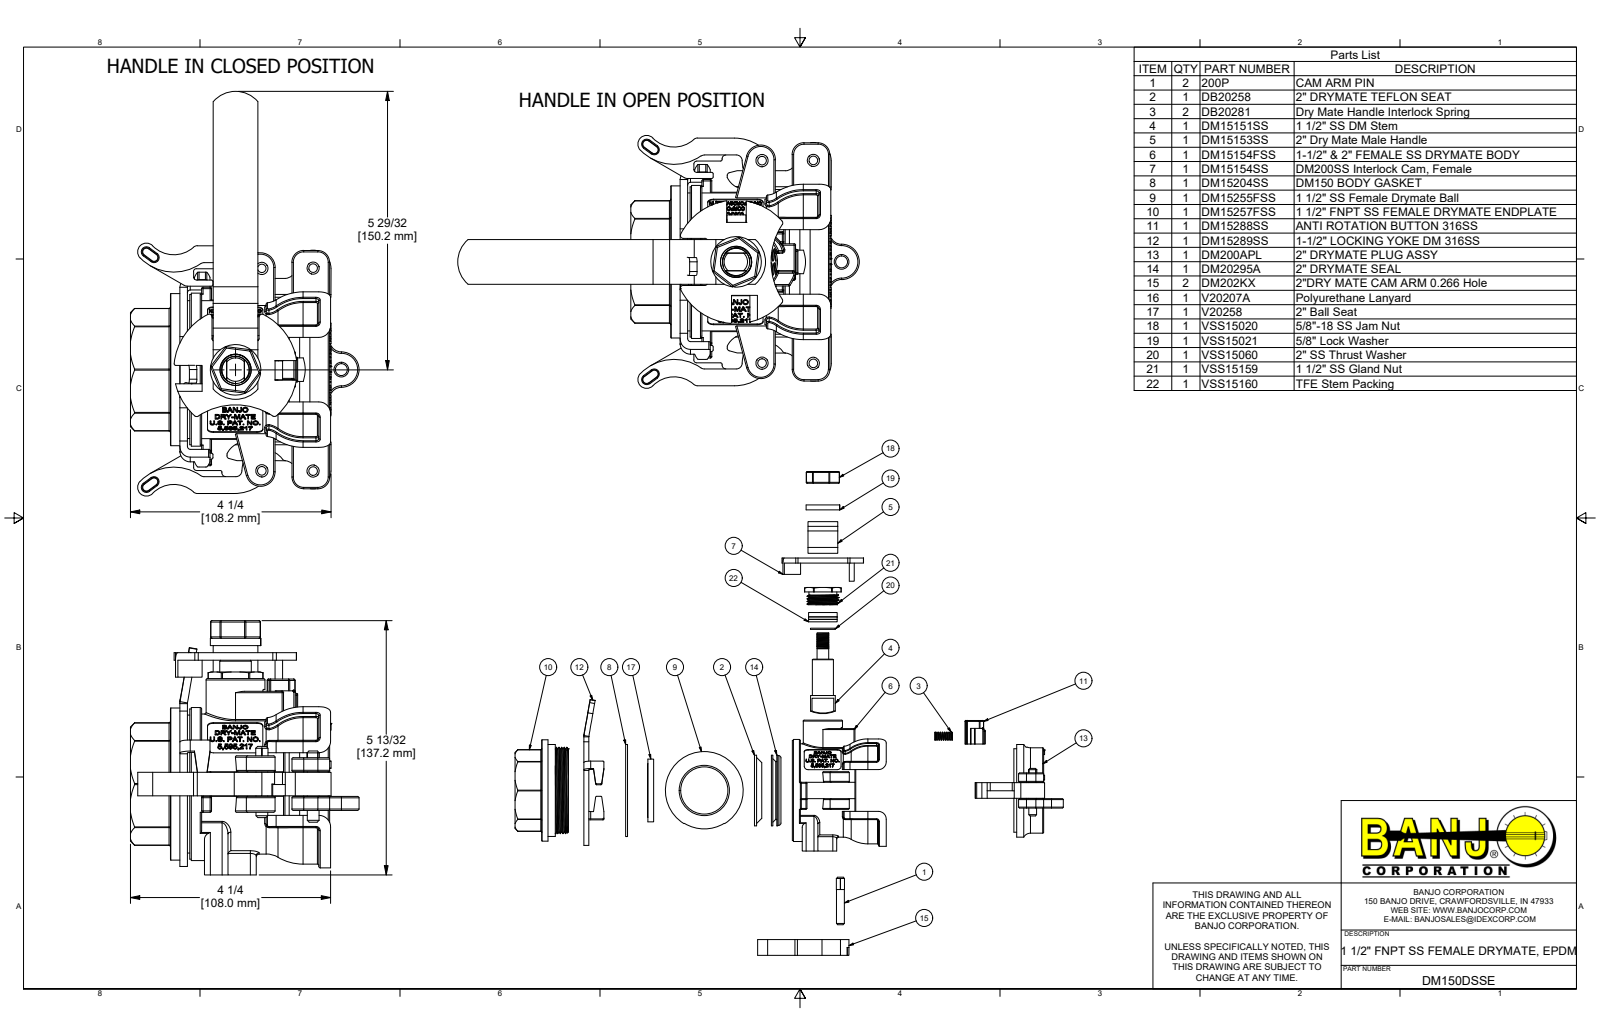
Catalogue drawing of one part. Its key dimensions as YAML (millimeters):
part_name: "DM150DSSE; DM15154FSS; DB20258; DB20281 (+8 more)"
step_written_by: "Autodesk Inventor 2019 (AUTOMOTIVE_DESIGN)"
units: millimeters
bodies: {solids: 35, faces: 2862, planar: 1145, cylindrical: 669, other: 1048}
overall_size: [798.9, 346.3, 137.3]
volume: 488300
surface_area: 444000
round_holes:
  - {diameter: 6.4, count: 5}
  - {diameter: 3.2, count: 3}
  - {diameter: 6.5, count: 2}
  - {diameter: 6.8, count: 2}
  - {diameter: 38.1, count: 2}
  - {diameter: 4.6, count: 1}
  - {diameter: 14.7, count: 1}
  - {diameter: 16.3, count: 1}
  - {diameter: 16.8, count: 1}
  - {diameter: 17, count: 1}
  - {diameter: 17.2, count: 1}
  - {diameter: 17.5, count: 1}
round_bosses_or_shafts:
  - {diameter: 6.6, count: 4}
  - {diameter: 6.3, count: 4}
  - {diameter: 7.1, count: 3}
  - {diameter: 88.9, count: 1}
  - {diameter: 82, count: 1}
  - {diameter: 81, count: 1}
  - {diameter: 75.6, count: 1}
  - {diameter: 75.4, count: 1}
partial_cylinders:
  - {radius: 0.8, count: 175}
  - {radius: 1.5, count: 25}
  - {radius: 3, count: 10}
  - {radius: 3.2, count: 10}
  - {radius: 6.4, count: 10}
  - {radius: 2, count: 9}
  - {radius: 0.8, count: 6}
  - {radius: 25.4, count: 6}
face_to_face_distances: [7.6, 4.1, 21.6, 3.8, 42.7, 55.4, 21.8, 21.8, 7.9, 20.6]
hole_center_spacings: [24.1, 27.7, 41.8, 56.4, 56.8, 57.1, 68.9, 69.5]
